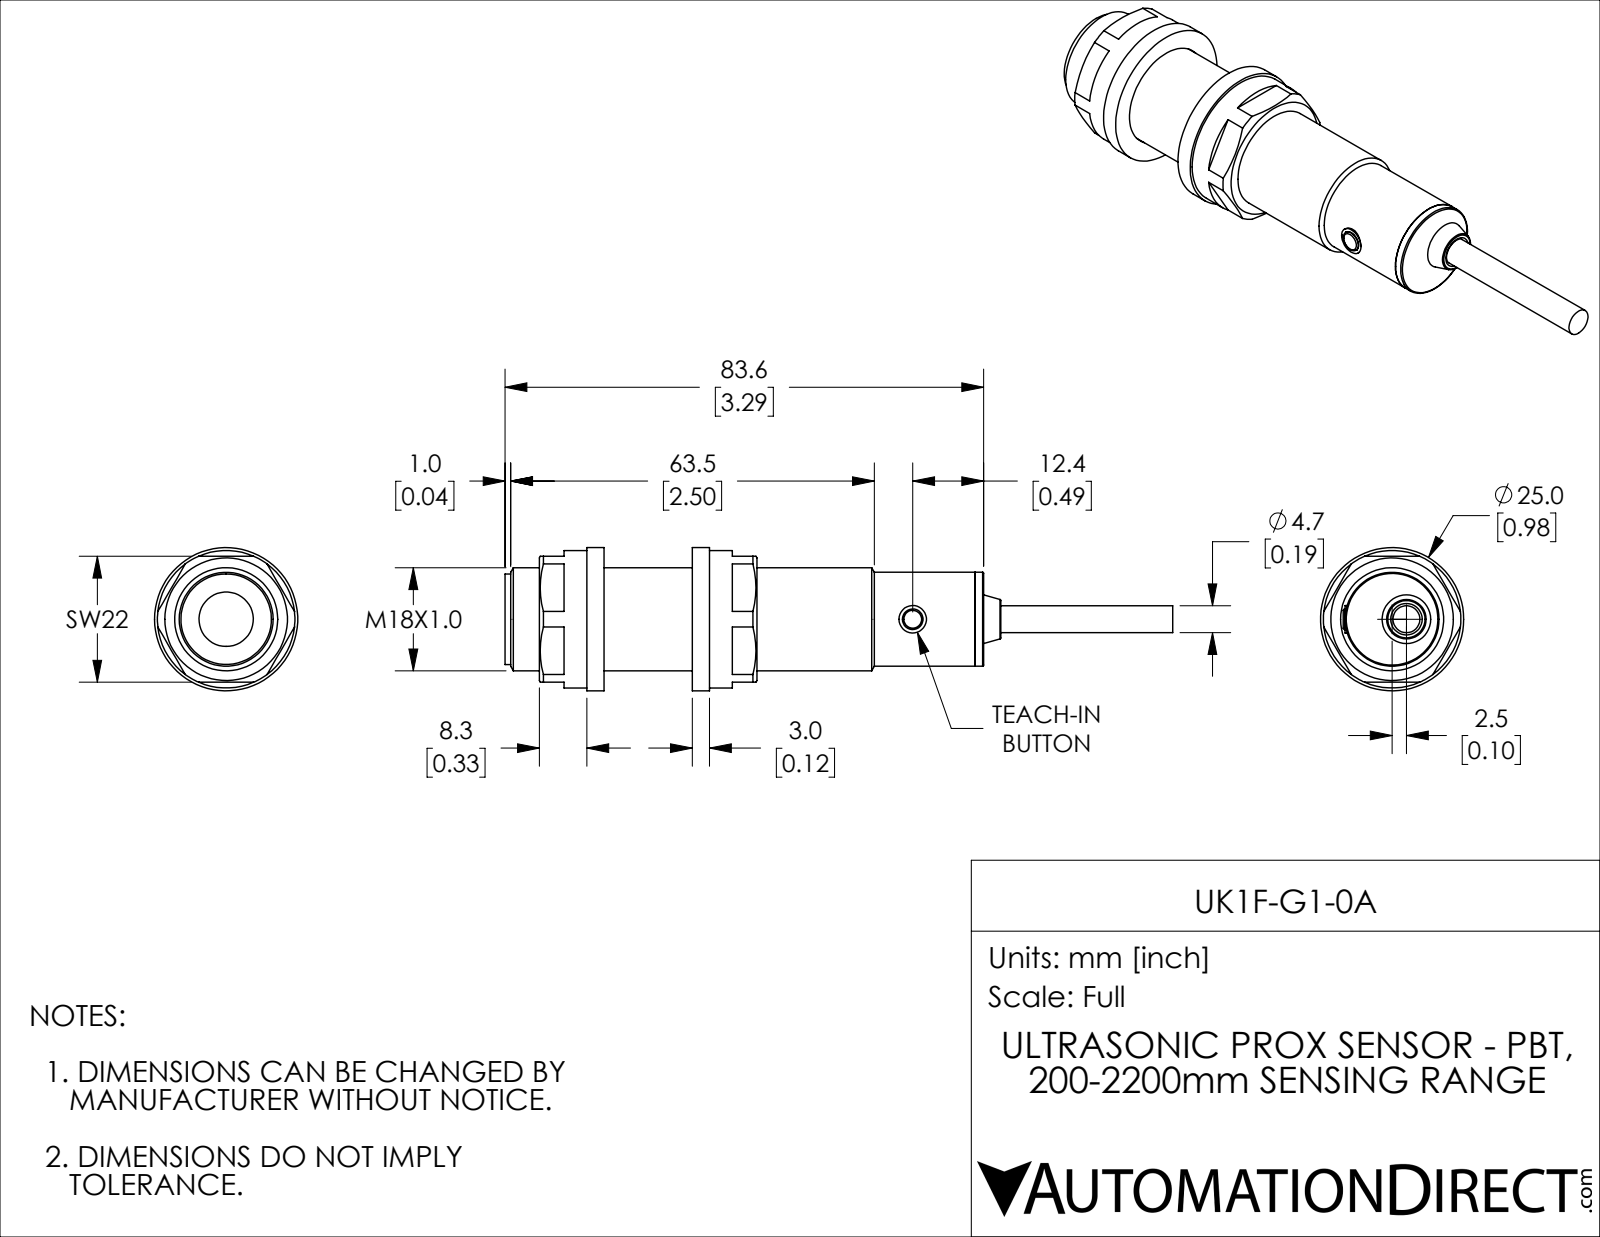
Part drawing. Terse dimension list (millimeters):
name: UK1F-G1-0A
written by: SolidWorks 2018 (AUTOMOTIVE_DESIGN)
unit: mm
bodies: 10 solids, 107 faces (49 planar, 40 cylindrical, 18 other)
size: 116.6 × 25 × 25
volume: 25 220 mm³; area: 11 419 mm²
holes: 2× ⌀4.7, 1× ⌀3.6, 1× ⌀9.5, 1× ⌀18, 1× ⌀18.2
bosses: 1× ⌀25, 1× ⌀24, 1× ⌀16.4, 1× ⌀15.8, 1× ⌀5.4, 1× ⌀4.8
face distances: 3, 18.4, 21.4, 67.8, 46.4, 13.3, 34.7, 81.1, 16.3, 64.8
hole spacings: 2.5
